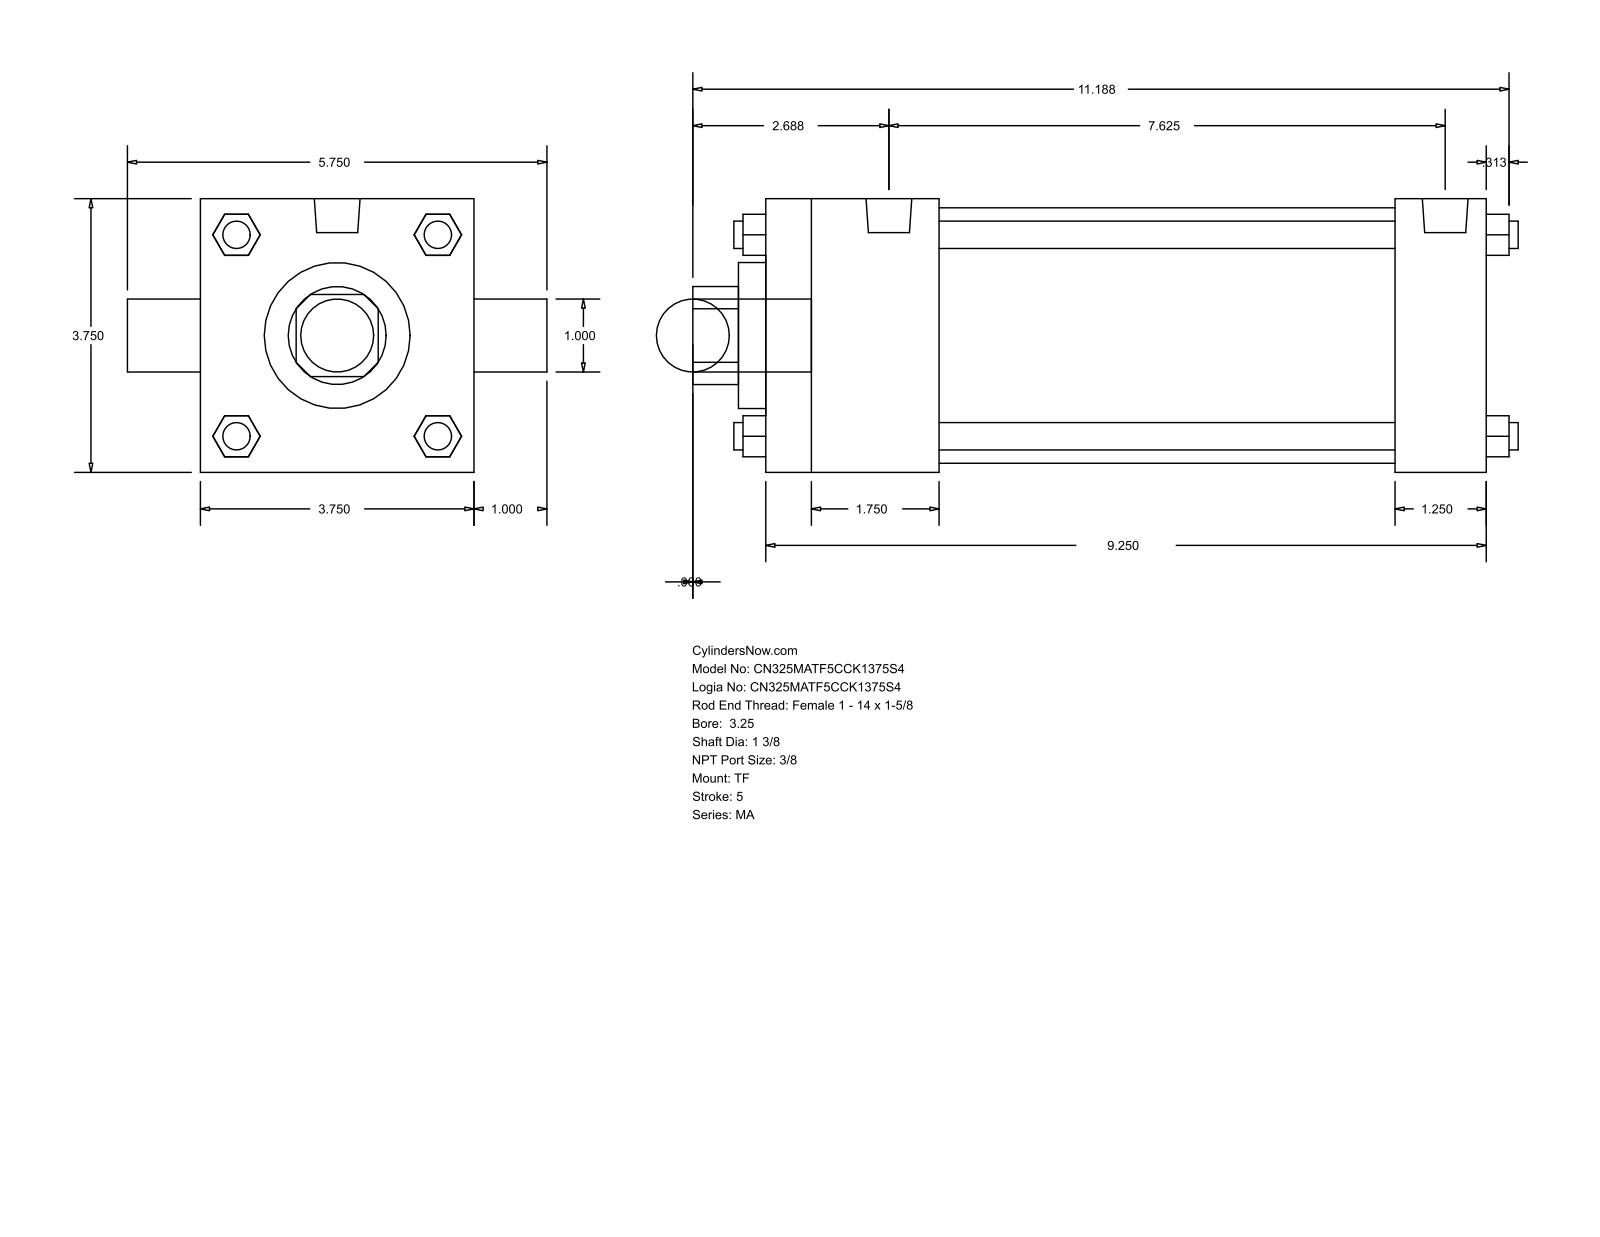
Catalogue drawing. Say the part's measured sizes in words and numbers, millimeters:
The part is named "MA_TF__0325_1.375". Its 3-D file was written by "GSSL Pune (CONFIG_CONTROL_DESIGN)". It is 0 solids with 120 faces: 92 planar, 28 cylindrical and 0 other. Overall it measures 287.34 by 146.05 by 95.25 millimeters. Round holes: 1 of diameter 25.4, 1 of diameter 34.92, 1 of diameter 50.8, 1 of diameter 88.9. Round bosses or shafts: 4 of diameter 9.53, 3 of diameter 11.11, 2 of diameter 15.93, 1 of diameter 25.4. Partial cylindrical surfaces (rounded edges, fillets, slot ends): 1 of radius 17.06. The main face-to-face distances are 95.24, 250.83, 60.32, 219.07, 158.75, 190.51, 31.76, 9.52, 69.84, 228.59.
